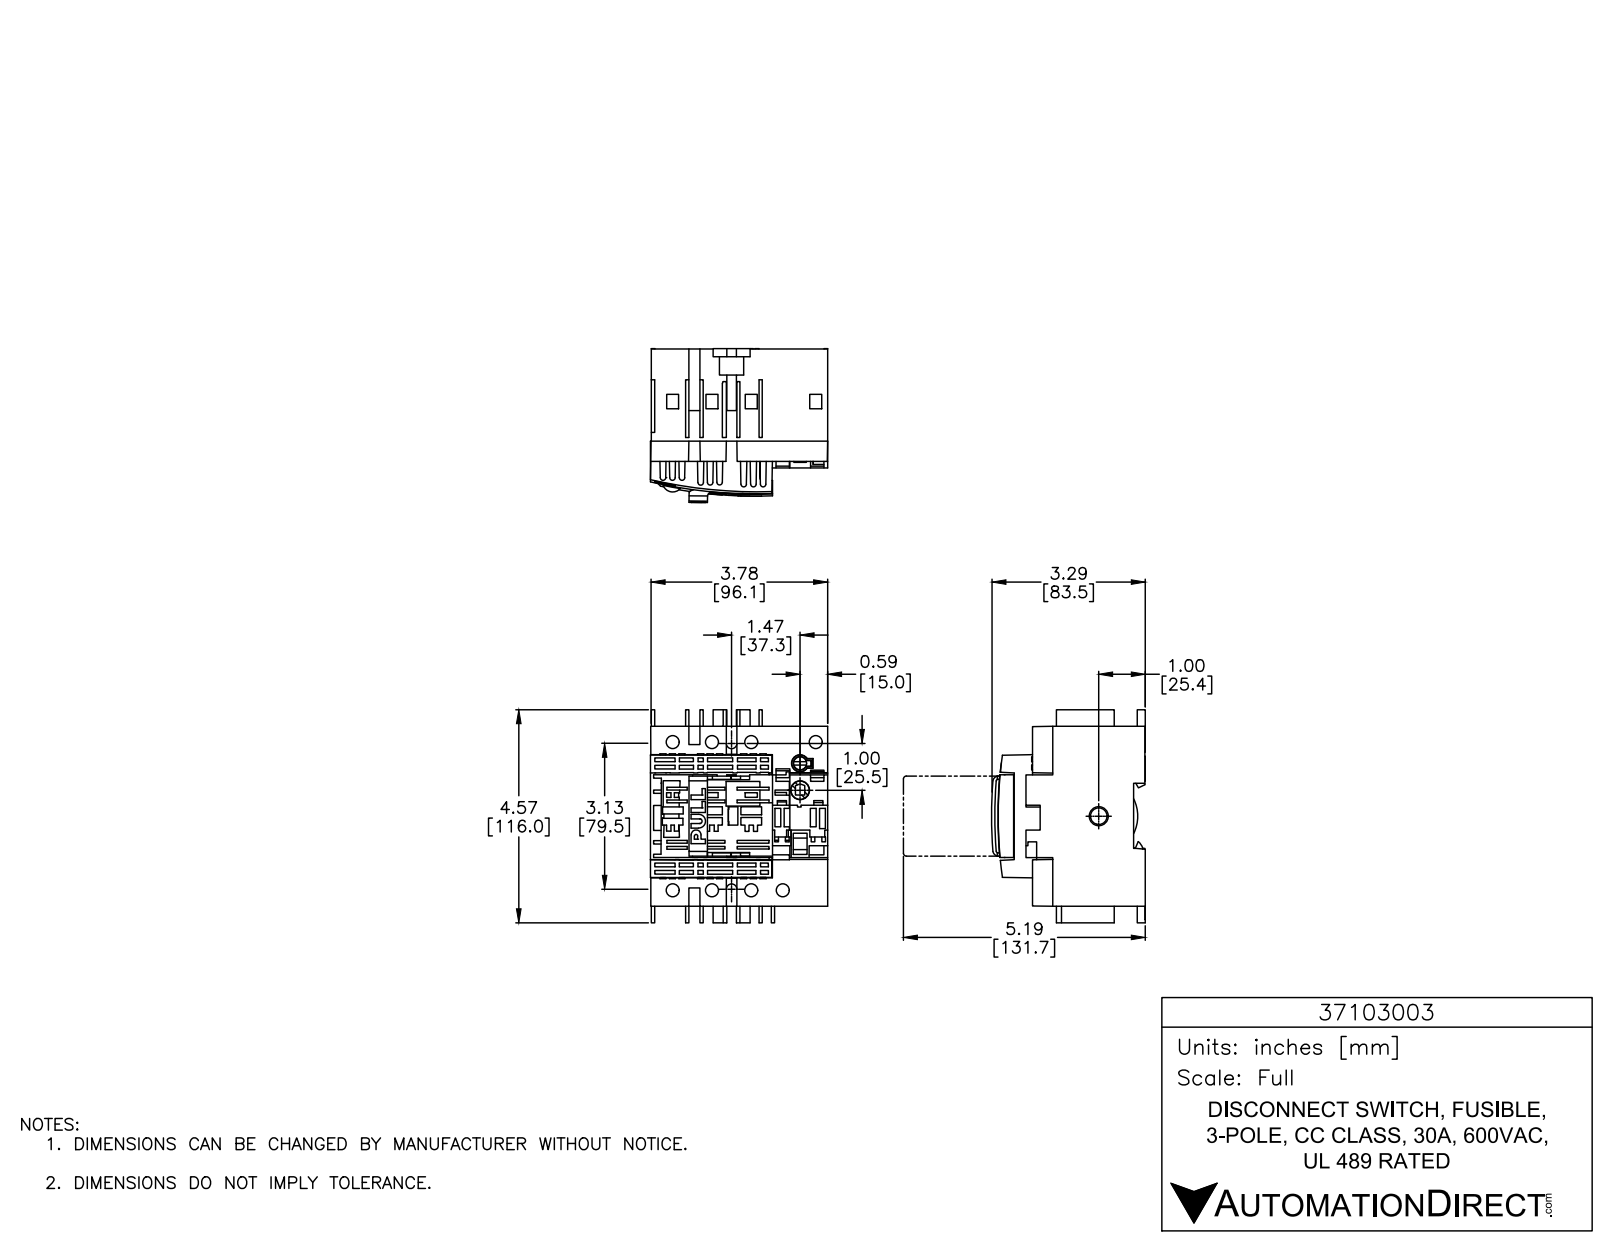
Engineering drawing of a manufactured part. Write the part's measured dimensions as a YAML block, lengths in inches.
part_name: "37103003"
step_written_by: "SolidWorks 2015 (AUTOMOTIVE_DESIGN)"
units: inches
bodies: {solids: 1, faces: 2010, planar: 1733, cylindrical: 167, other: 110}
overall_size: [4.567, 3.799, 3.299]
volume: 32.14
surface_area: 178.1
round_holes:
  - {diameter: 0.276, count: 8}
  - {diameter: 0.146, count: 4}
  - {diameter: 0.277, count: 2}
  - {diameter: 0.287, count: 1}
  - {diameter: 0.291, count: 1}
  - {diameter: 0.354, count: 1}
  - {diameter: 0.362, count: 1}
  - {diameter: 0.386, count: 1}
  - {diameter: 0.402, count: 1}
  - {diameter: 0.409, count: 1}
round_bosses_or_shafts:
  - {diameter: 0.394, count: 1}
  - {diameter: 0.276, count: 1}
partial_cylinders:
  - {radius: 0.02, count: 20}
  - {radius: 0.059, count: 14}
  - {radius: 0.039, count: 11}
  - {radius: 0.051, count: 8}
  - {radius: 0.148, count: 4}
  - {radius: 0.118, count: 3}
  - {radius: 0.083, count: 2}
  - {radius: 0.102, count: 2}
face_to_face_distances: [3.78, 3.858, 1.128, 2.791, 0.244, 2.409, 0.382, 2.165, 2.547, 1.732]
hole_center_spacings: [0.843, 3.287, 3.177, 0.375, 1.188, 1.685, 2.025, 2.831]
